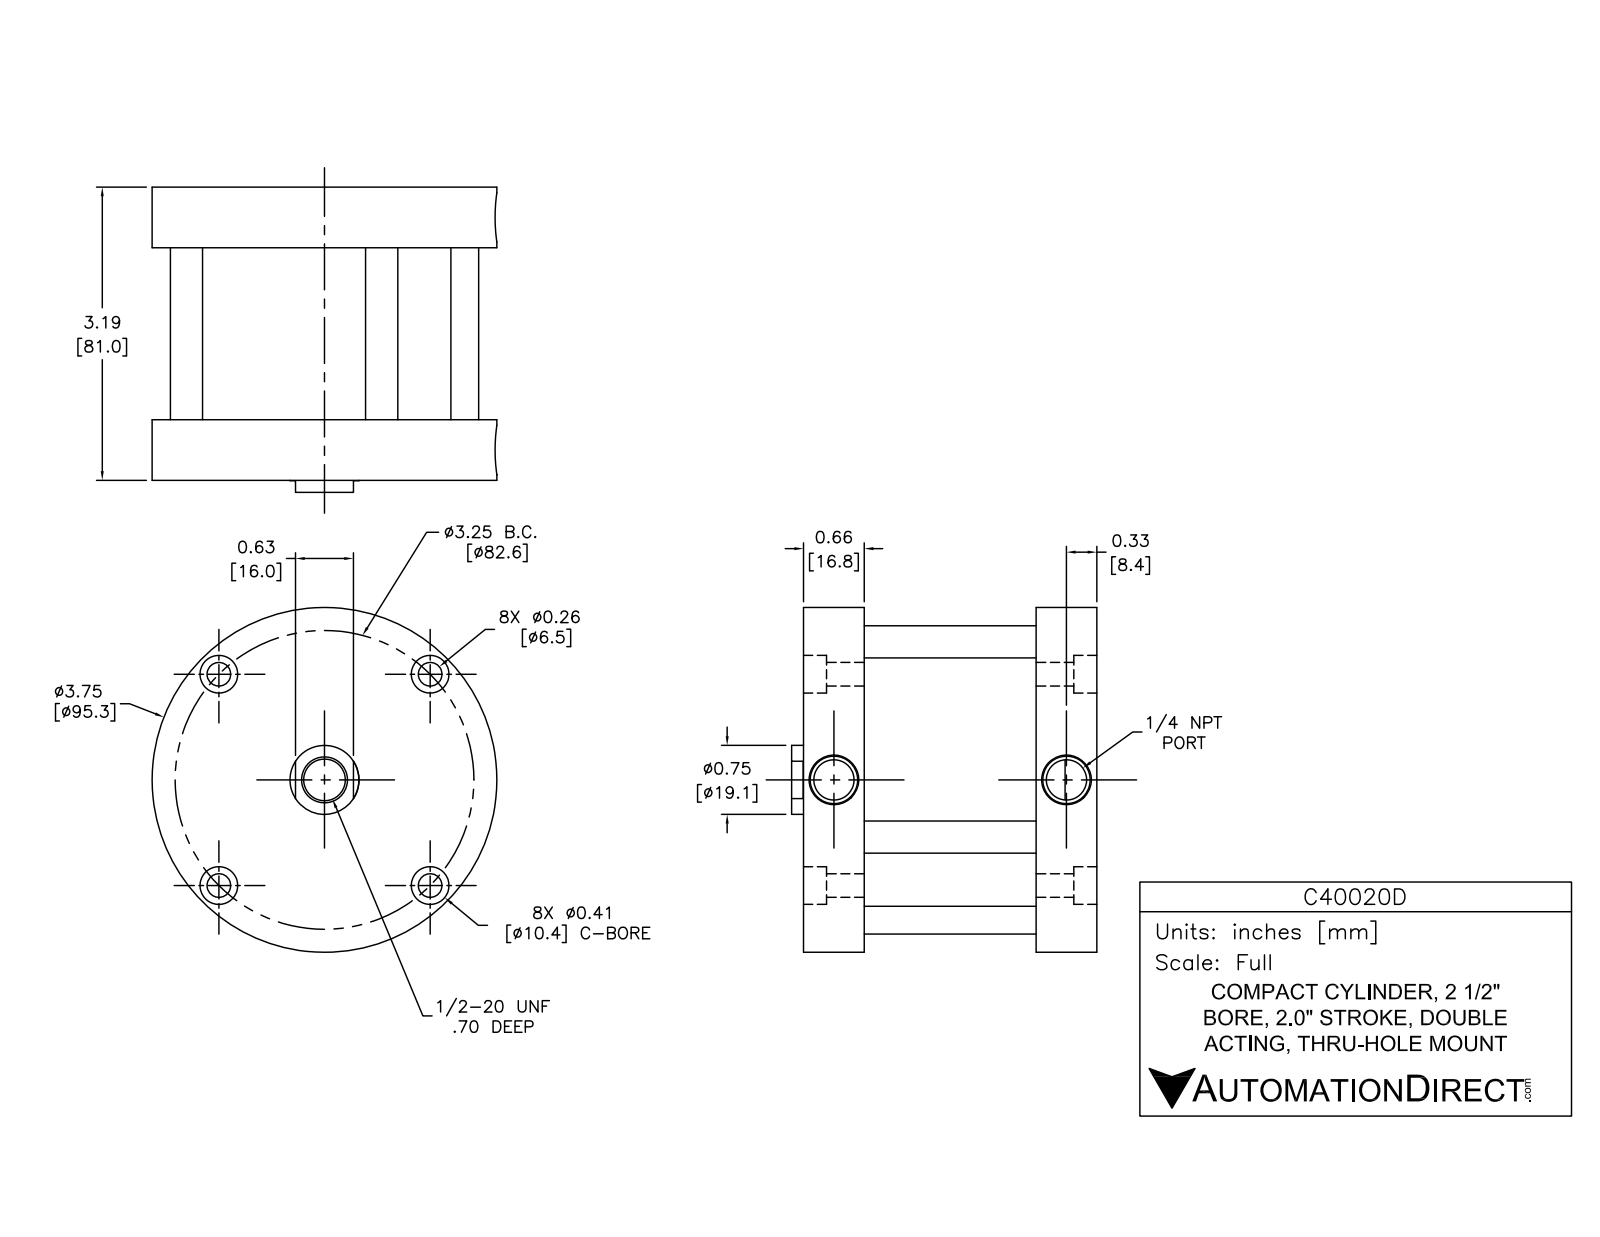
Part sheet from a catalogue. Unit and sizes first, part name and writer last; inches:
Units: inches
Overall size (bounding box): 3.75 × 3.75 × 3.32
Round holes (diameter × count): ⌀0.225 ×4, ⌀0.281 ×4, ⌀0.406 ×4, ⌀0.218 ×2, ⌀0.446 ×1, ⌀0.75 ×1, ⌀0.752 ×1, ⌀2.5 ×1, ⌀2.639 ×1
Round bosses / shafts (diameter × count): ⌀0.45 ×4, ⌀0.225 ×4, ⌀3.75 ×1
Main face-to-face distances: 0.387, 2.803, 3.19, 2.416, 2.53, 2.143, 0.273, 0.66, 0.66, 0.273
Hole centre spacings: 0.48, 1.625, 1.625, 1.933, 2.298, 2.298, 2.613, 3.215
Volume: 16.35 in³ · Surface area: 147.2 in²
Bodies: 9 solids, 165 faces (49 planar, 98 cylindrical, 18 other)
Part name (STEP PRODUCT): C40020D; C40020D-FO1_BM_r; C40020D-FO1_BM_tube; C40020D-rod_part (+3 more)
STEP written by: SolidWorks 2014 (AUTOMOTIVE_DESIGN)
